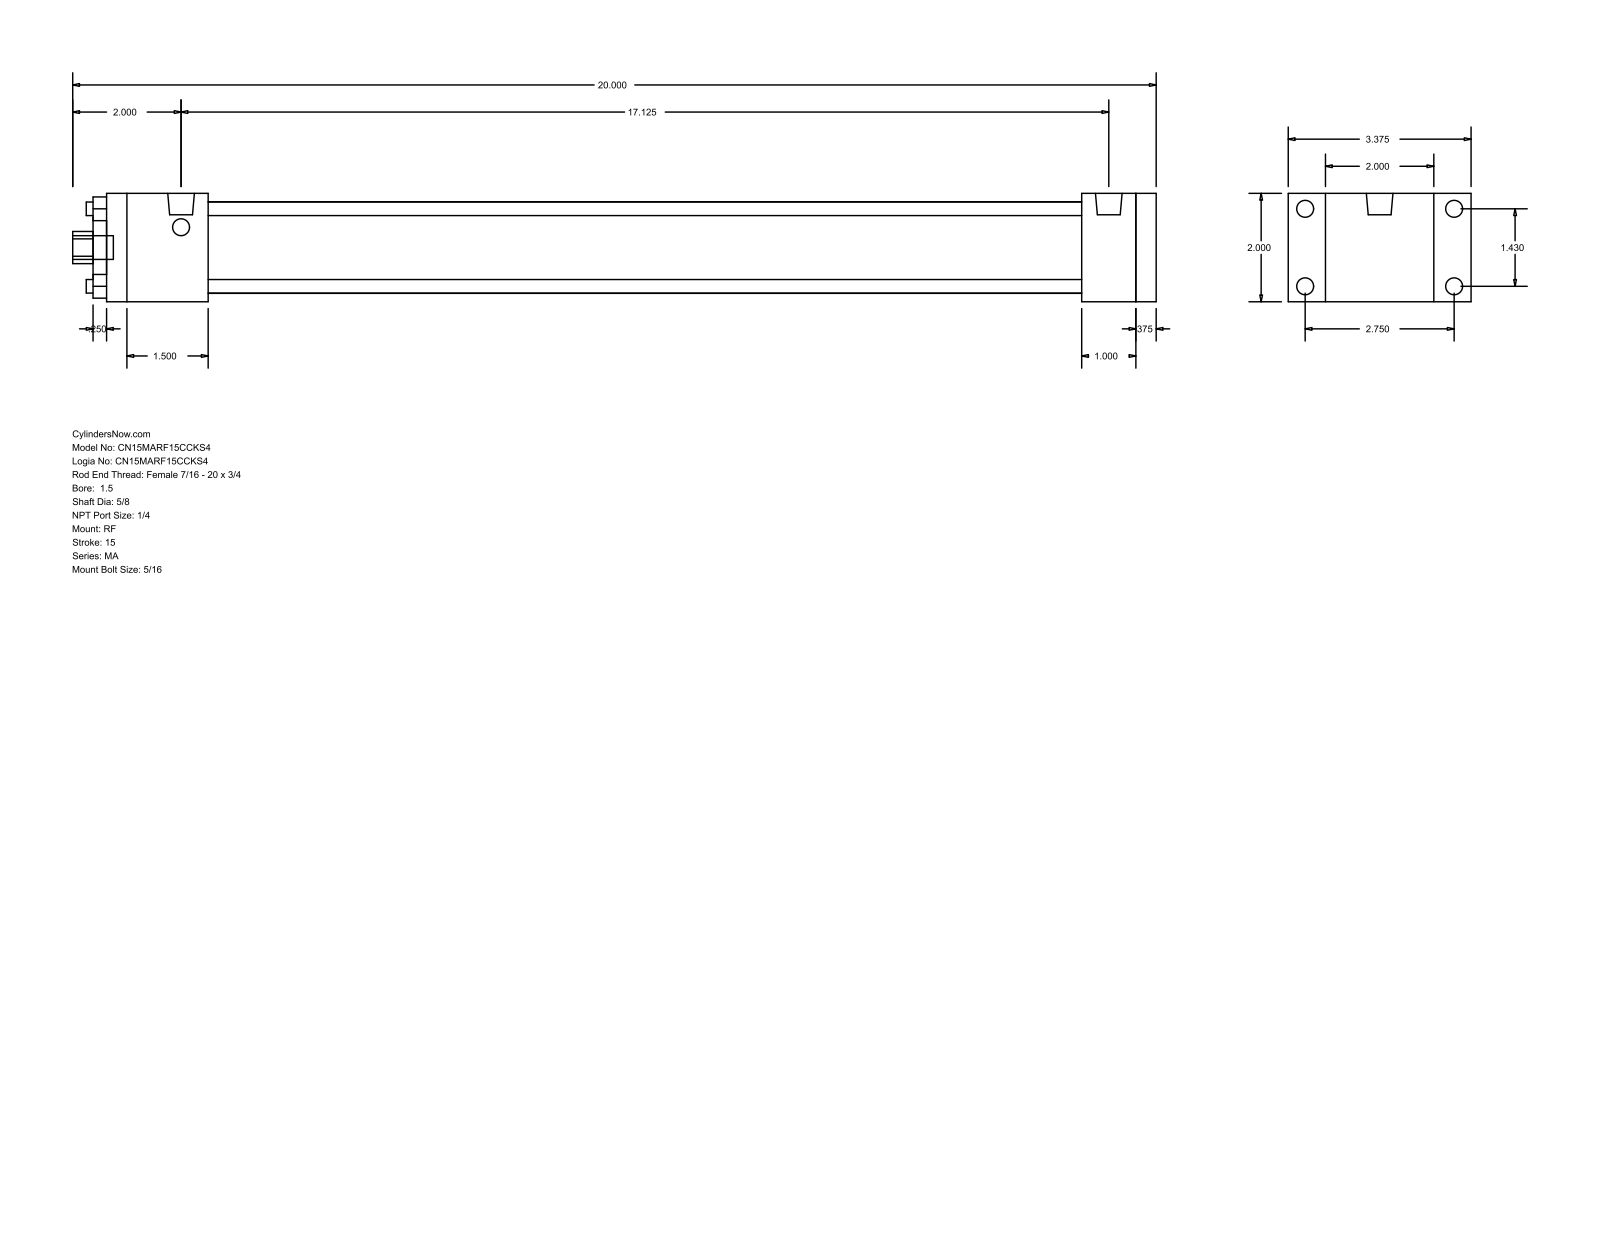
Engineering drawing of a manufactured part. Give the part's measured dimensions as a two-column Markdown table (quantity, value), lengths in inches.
| quantity | value |
| --- | --- |
| part name | MA_RF__0150_0.625 |
| STEP written by | GSSL Pune (CONFIG_CONTROL_DESIGN) |
| units | inches |
| bodies | 0 solids, 92 faces (64 planar, 28 cylindrical, 0 other) |
| overall size | 20 × 3.375 × 2 |
| round holes (diameter × count) | 0.25 × 4, 0.625 × 1, 1.125 × 1, 1.69 × 1 |
| round bosses / shafts (diameter × count) | 0.313 × 8, 0.492 × 2, 0.437 × 1 |
| partial cylindrical surfaces (radius × count) | 0.297 × 1 |
| main face-to-face distances | 2, 0.375, 19, 19.375, 18, 1, 1.375, 1.875, 16.125, 17.125 |
| hole center spacings | 1.011, 1.43, 2.022 |
